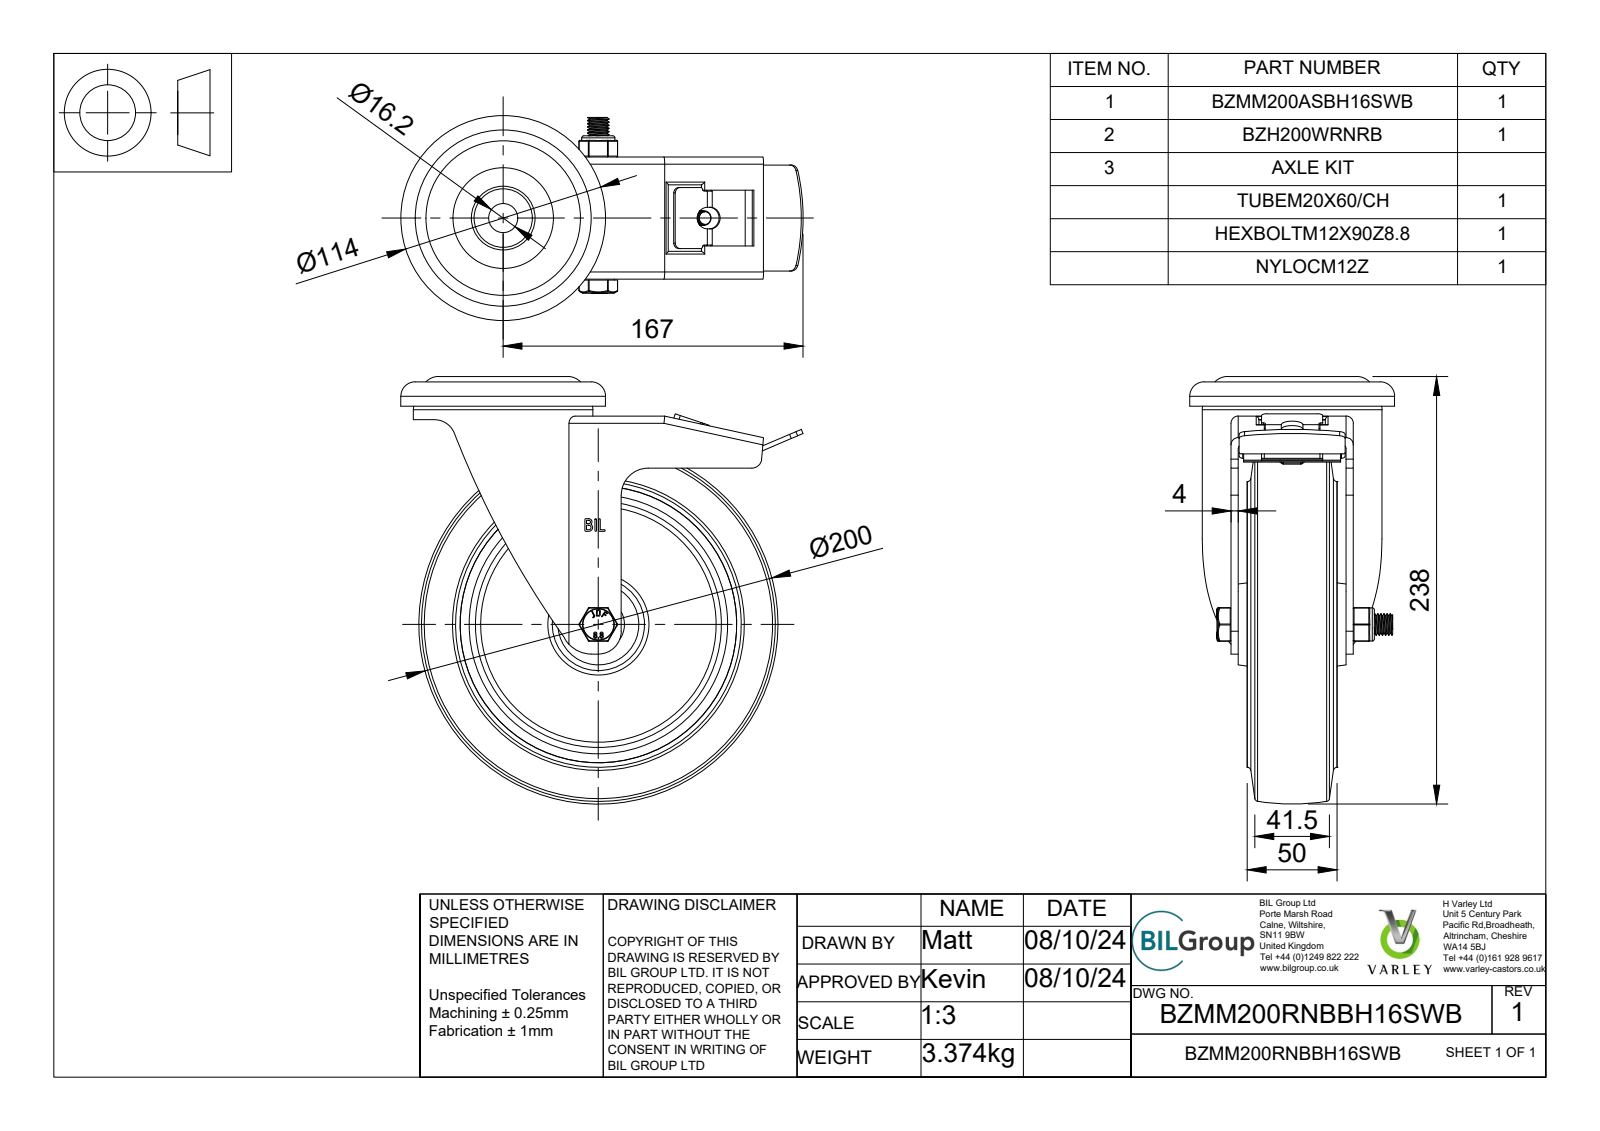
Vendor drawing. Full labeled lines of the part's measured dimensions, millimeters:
Part name (STEP PRODUCT): BZMM200RNBBH16SWB v3; BZMM200ASBH16SWB v1; ZINC PLATED, PRESSED STEEL HEAD; ZINC PLATED, PRESSED STEEL FORKS (+8 more)
STEP written by: Autodesk Translation Framework v13.20.0.188 (AUTOMOTIVE_DESIGN)
Units: millimetres
Bodies: 22 solids, 646 faces (304 planar, 235 cylindrical, 107 other)
Overall size (bounding box): 238 × 224 × 114
Volume: 1 200 000 mm³ · Surface area: 330 387 mm²
Round holes (diameter × count): ⌀4.7 ×10, ⌀8 ×1, ⌀12 ×1, ⌀12.2 ×1, ⌀12.5 ×1, ⌀14 ×1, ⌀16.2 ×1, ⌀20 ×1, ⌀29 ×1, ⌀41 ×1, ⌀52 ×1, ⌀92 ×1
Round bosses / shafts (diameter × count): ⌀4.5 ×10, ⌀159 ×1, ⌀114 ×1, ⌀100 ×1, ⌀74 ×1, ⌀47 ×1, ⌀32.5 ×1, ⌀19.9 ×1
Partial cylindrical surfaces — rounded edges, fillets, slot ends (radius × count): R1 ×25, R0.5 ×24, R2 ×12, R4 ×7, R1.5 ×6, R0.47 ×4, R0.9 ×4, R0.89 ×2
Main face-to-face distances: 9, 29.5, 4, 34.5, 25.5, 38.5, 64, 5, 55, 59
Hole centre spacings: 12.25, 14.4, 19.82, 23.3, 7.57, 24.5, 7.58
